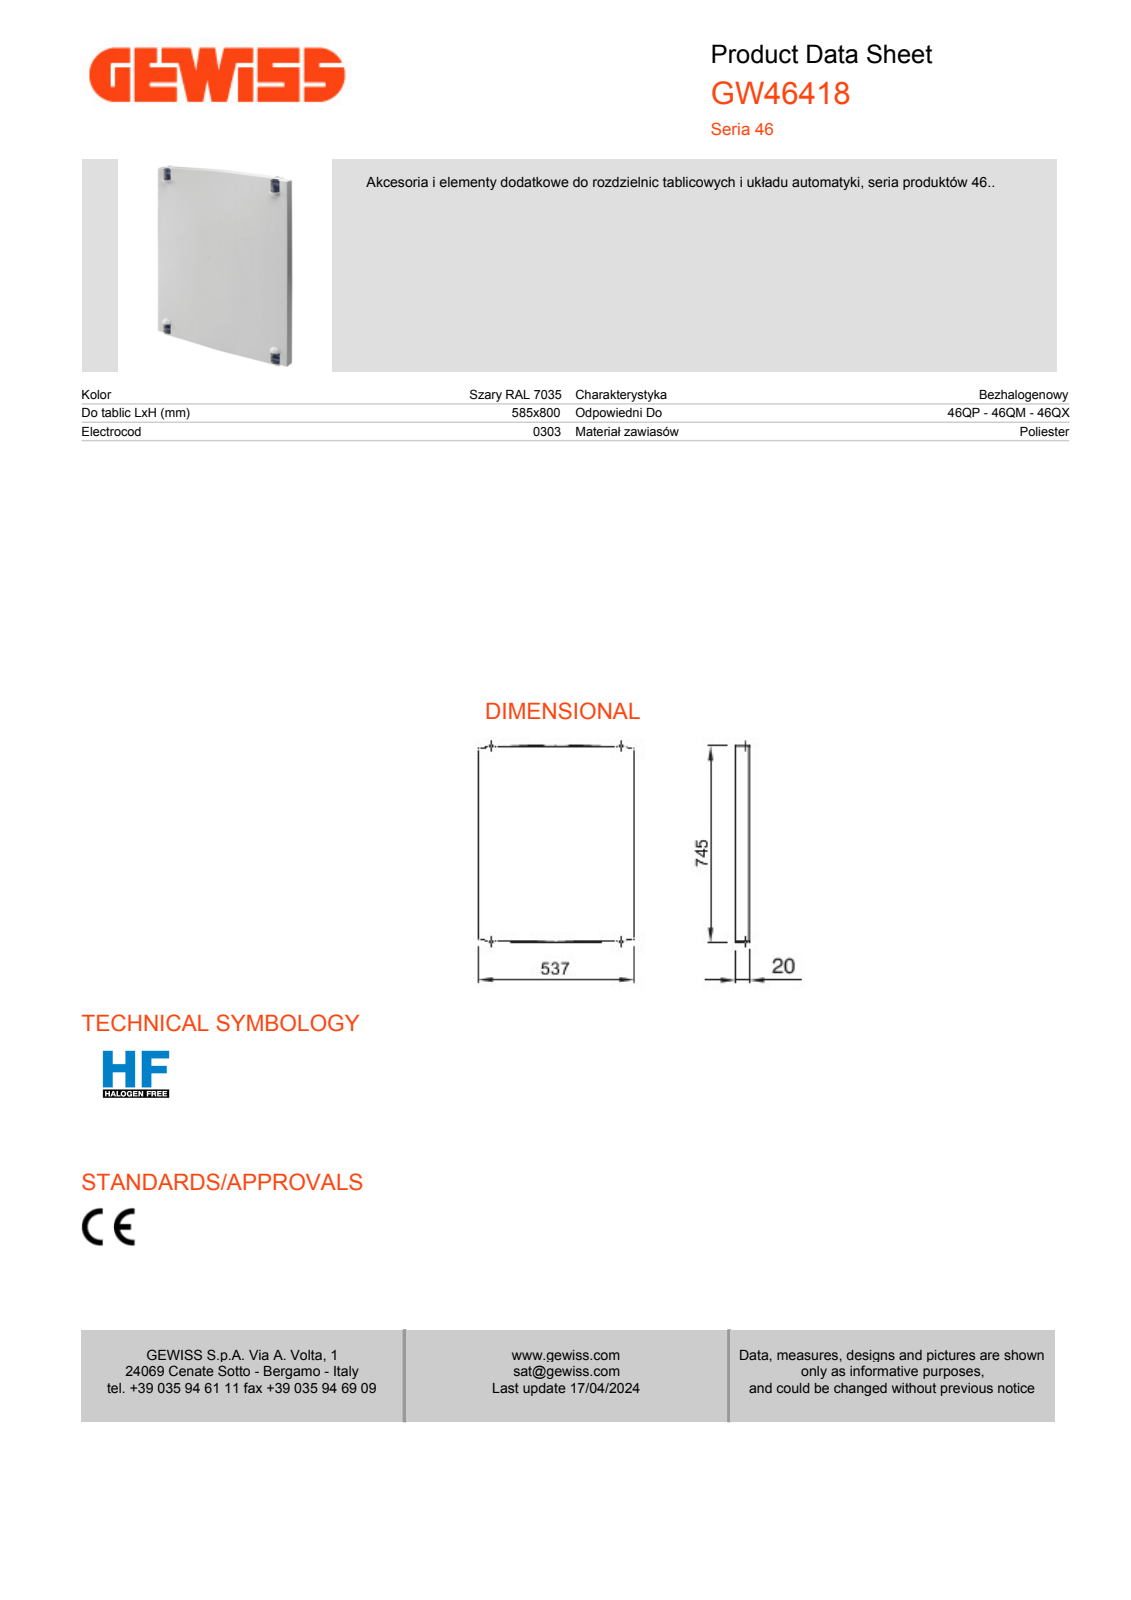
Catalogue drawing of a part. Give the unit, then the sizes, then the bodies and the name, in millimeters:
Units: millimetres
Overall size (bounding box): 751.86 × 536.86 × 30.32
Round holes (diameter × count): ⌀8.4 ×2
Round bosses / shafts (diameter × count): ⌀12.1 ×2
Partial cylindrical surfaces — rounded edges, fillets, slot ends (radius × count): R2 ×20, R3 ×4, R5 ×2
Main face-to-face distances: 3, 747.07, 532.36, 532.37, 20, 17, 2.5, 17.5, 14.5, 477
Hole centre spacings: 477
Volume: 1 353 000 mm³ · Surface area: 901 815 mm²
Bodies: 1 solid, 191 faces (123 planar, 48 cylindrical, 20 other)
Part name (STEP PRODUCT): GW46418
STEP written by: CREO PARAMETRIC BY PTC INC, 2020354 (CONFIG_CONTROL_DESIGN)
